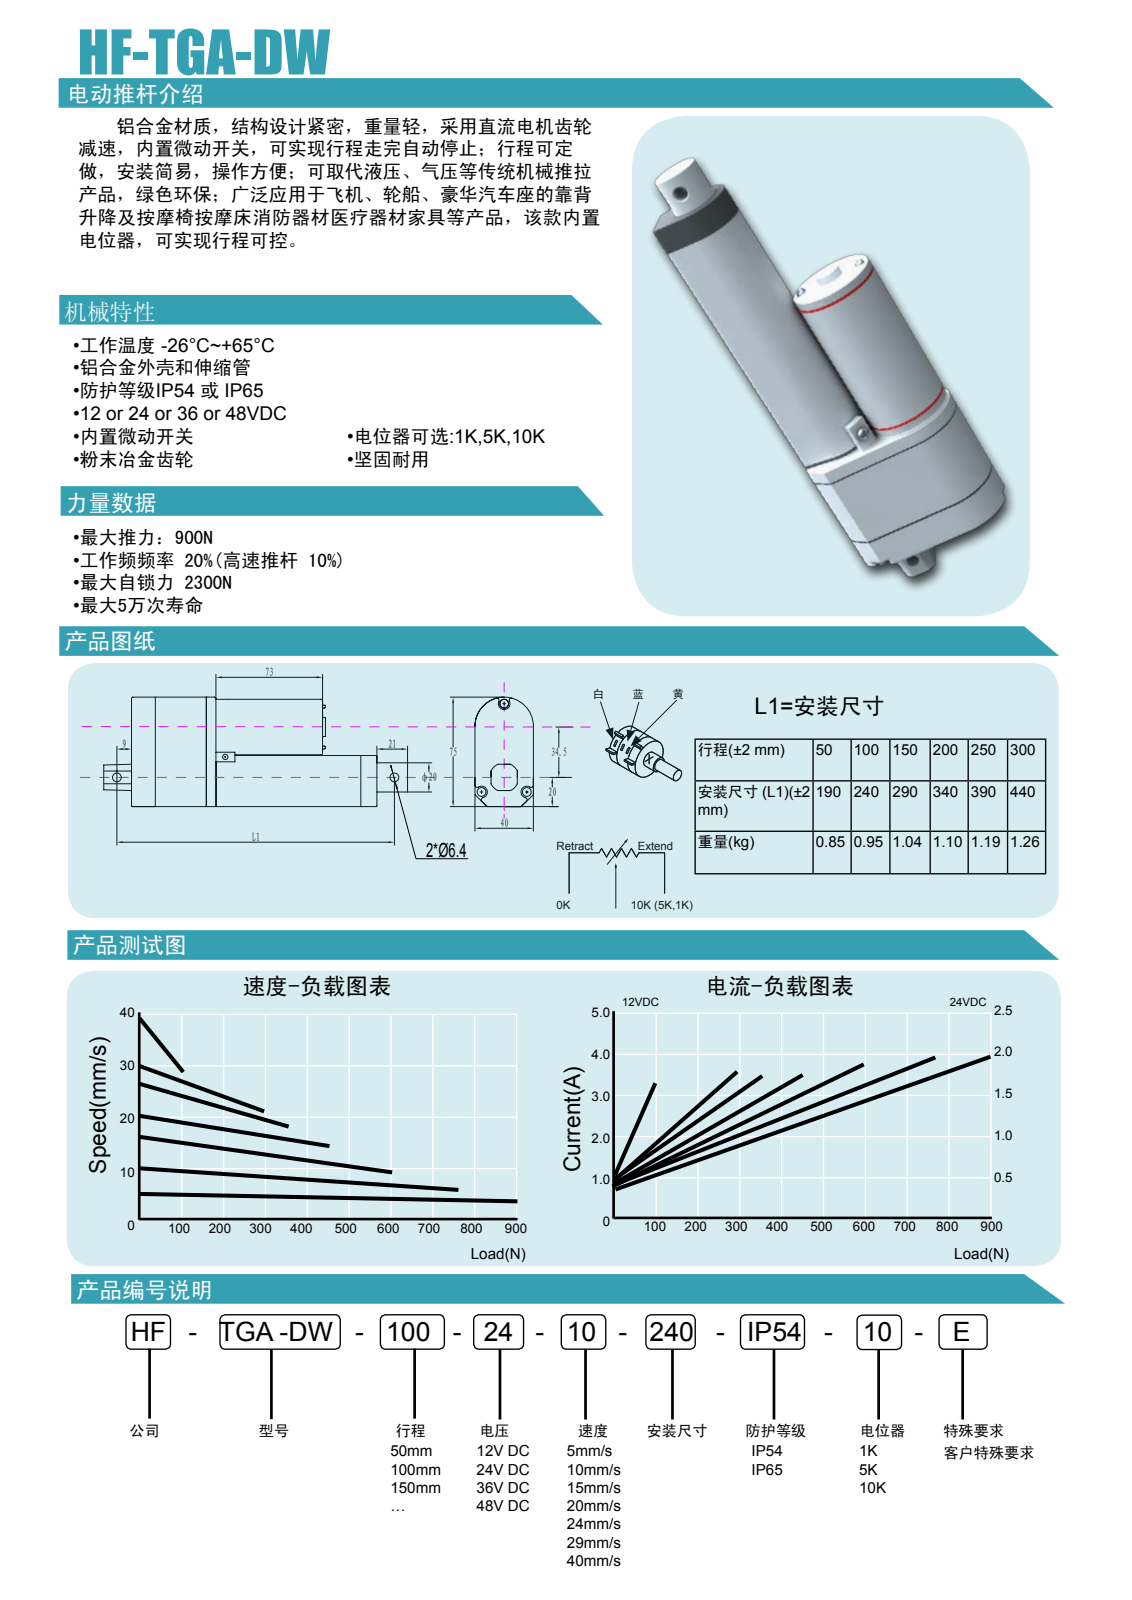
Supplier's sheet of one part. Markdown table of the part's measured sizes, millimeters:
| quantity | value |
| --- | --- |
| part name | UP; END; MOTER; WAIKE (+3 more) |
| STEP written by | PRO/ENGINEER BY PARAMETRIC TECHNOLOGY CORPORATION, 2008380 (CONFIG_CONTROL_DESIGN) |
| units | millimeters |
| bodies | 6 solids, 328 faces (148 planar, 87 cylindrical, 93 other) |
| overall size | 258 × 75.08 × 40.32 |
| volume | 312 624 mm³ |
| surface area | 83 106 mm² |
| round holes (diameter × count) | 6 × 1, 6.4 × 1, 20 × 1 |
| round bosses / shafts (diameter × count) | 6 × 3, 5 × 2, 38 × 1, 13 × 1 |
| partial cylindrical surfaces (radius × count) | 1 × 32, 0.5 × 13, 4 × 3, 1 × 1, 10 × 1, 13 × 1, 14.99 × 1, 17 × 1 |
| main face-to-face distances | 35, 2.01, 51.3, 16.3, 40, 6.5, 41.5, 57.8, 73, 79.5 |
